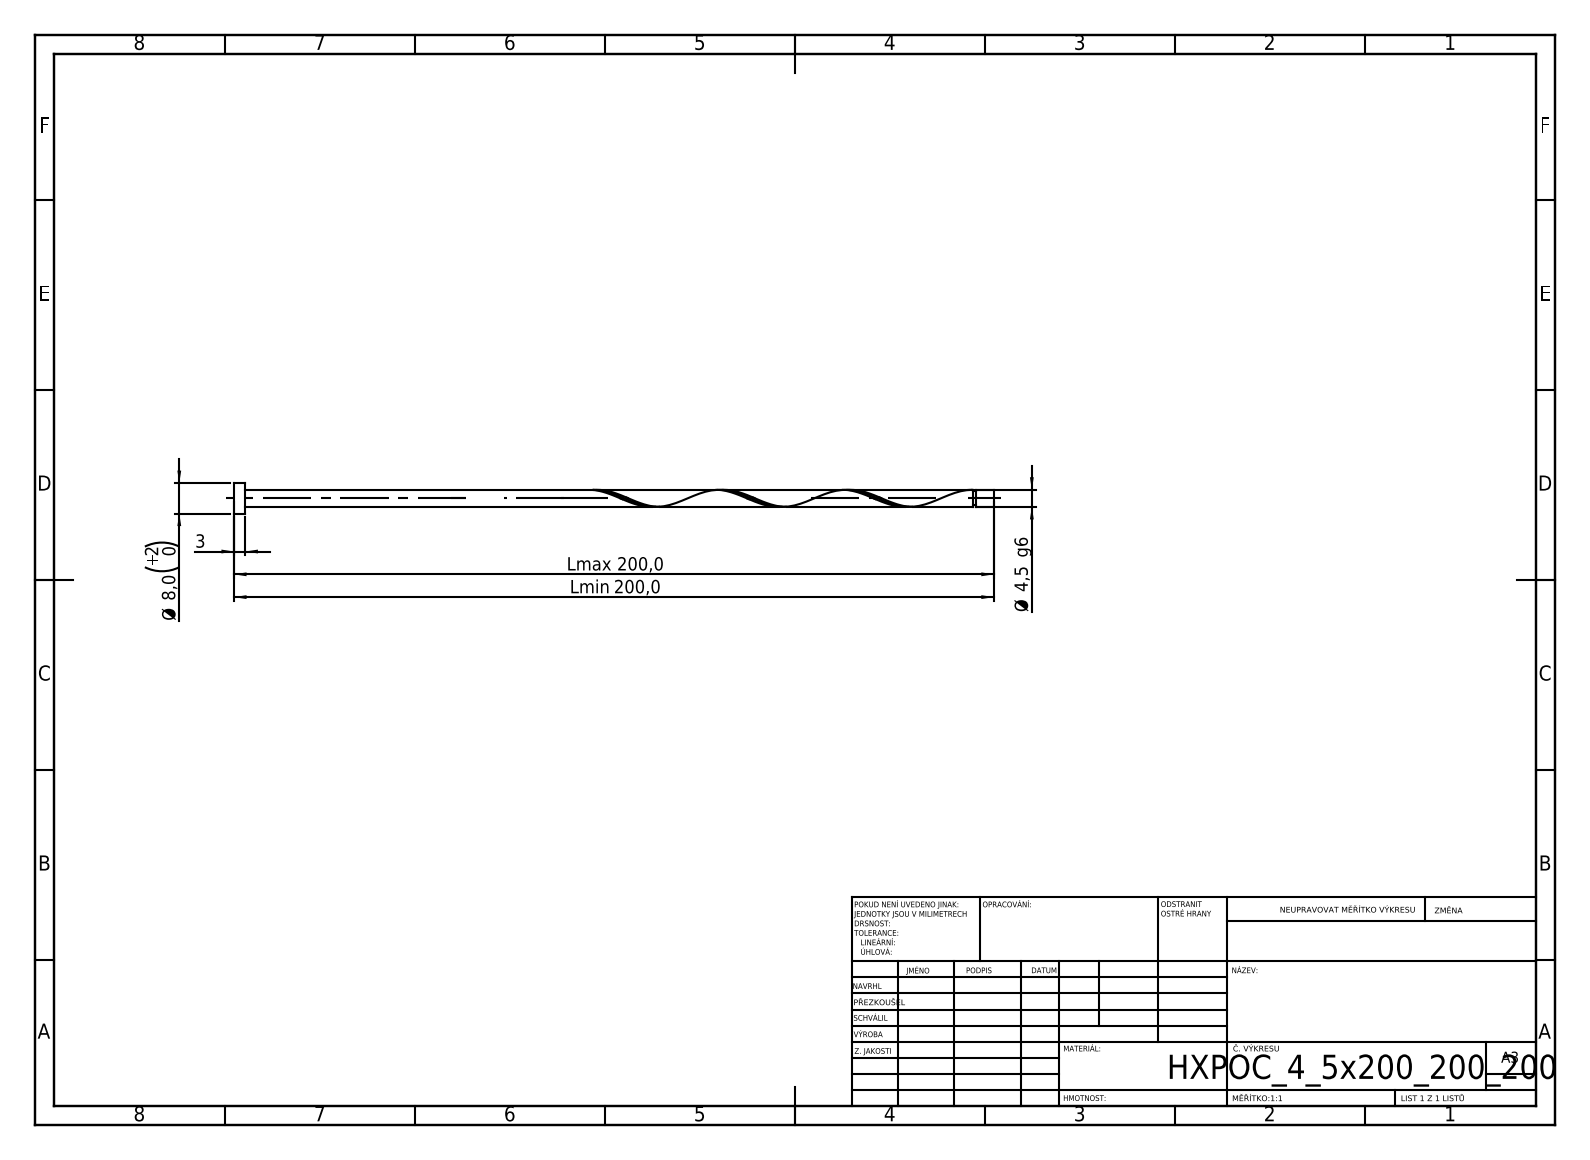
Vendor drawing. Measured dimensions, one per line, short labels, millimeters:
written by: SolidWorks 2019 (CONFIG_CONTROL_DESIGN)
unit: mm
bodies: 1 solid, 21 faces (6 planar, 14 cylindrical, 1 other)
size: 200 × 8 × 8
volume: 3 248 mm³; area: 3 017 mm²
bosses: 1× ⌀8, 1× ⌀4.5, 1× ⌀3.6
face distances: 3, 200, 197, 195.3, 192.3, 4.7, 194.4, 191.4, 0.9, 5.6
